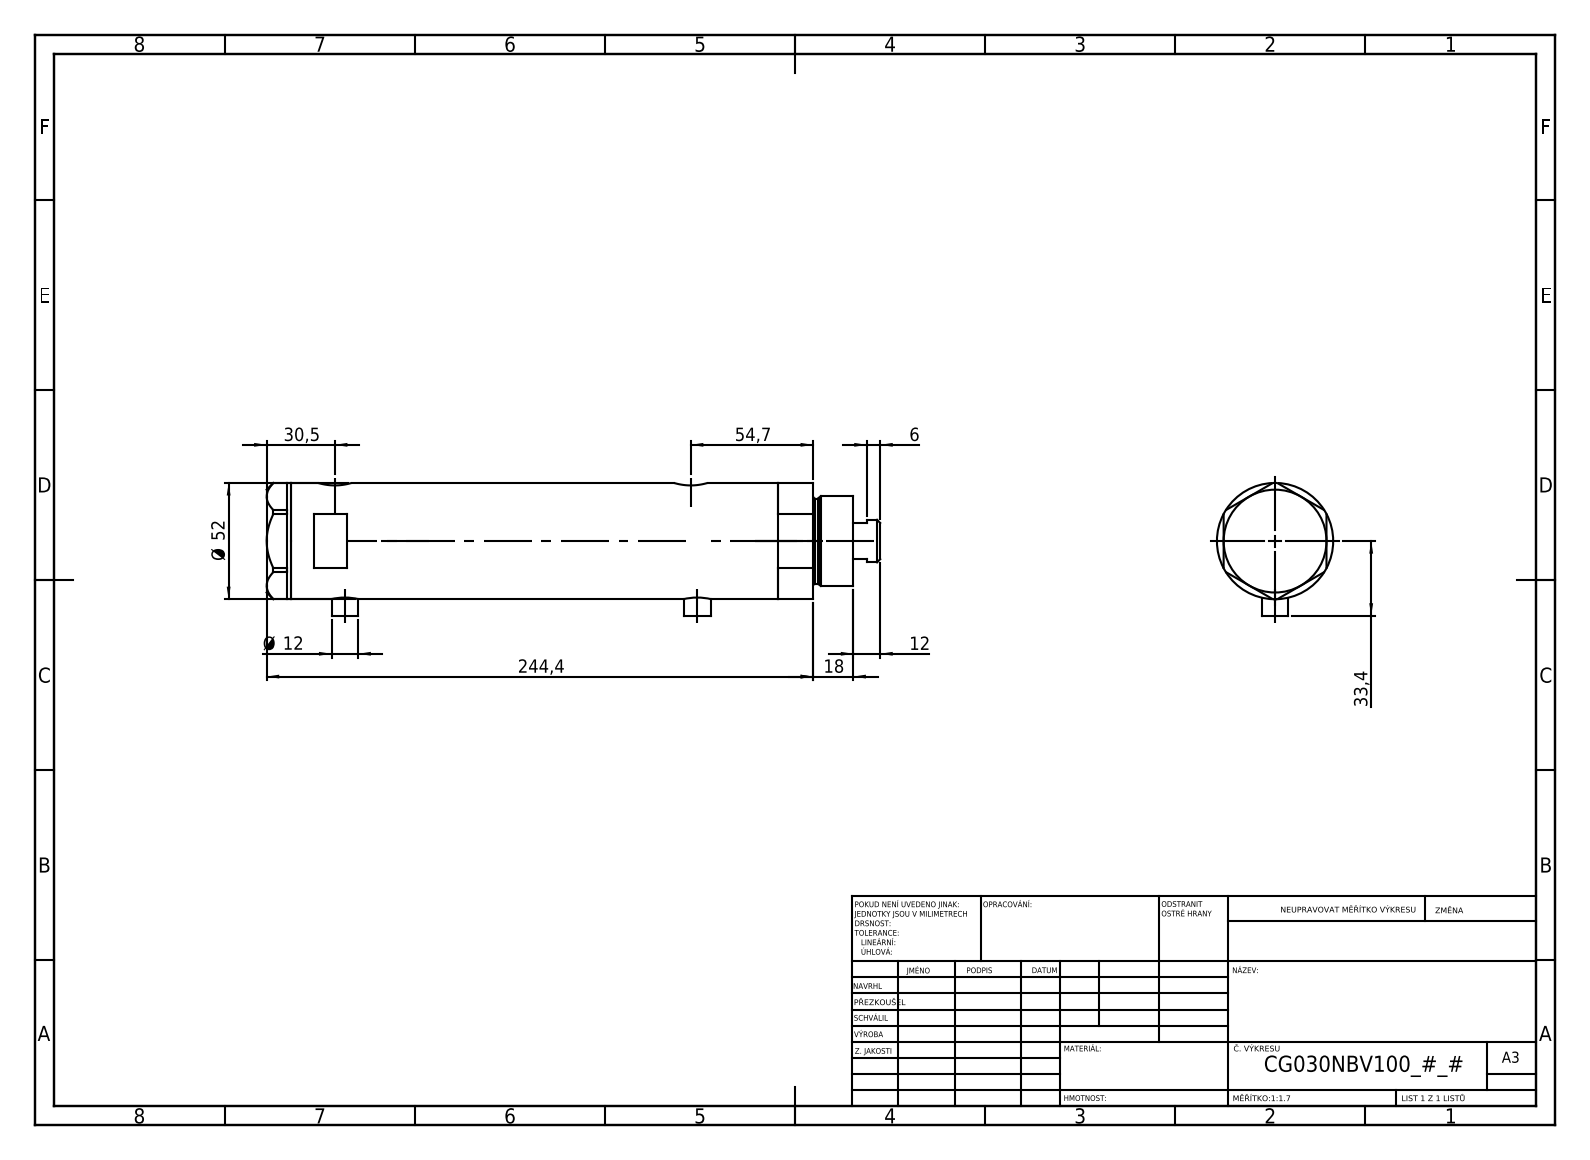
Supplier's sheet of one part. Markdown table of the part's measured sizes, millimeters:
| quantity | value |
| --- | --- |
| part name | V270CG_BACK; V270CG_MIDDLE; V270CG_FRONT; V270CG_VC |
| STEP written by | SolidWorks 2019 (CONFIG_CONTROL_DESIGN) |
| units | millimeters |
| bodies | 4 solids, 134 faces (65 planar, 49 cylindrical, 20 other) |
| overall size | 274.4 × 59.4 × 52 |
| volume | 498 565 mm³ |
| surface area | 106 603 mm² |
| round holes (diameter × count) | 9.73 × 2, 12.5 × 2, 15 × 2, 6.5 × 1, 20 × 1, 21.5 × 1, 30 × 1, 33 × 1, 44 × 1 |
| round bosses / shafts (diameter × count) | 12 × 2, 52 × 1, 40 × 1, 38 × 1, 19 × 1 |
| main face-to-face distances | 181.5, 23.8, 157.7, 11, 34.8, 192.5, 46, 228.9, 217.9, 194.1 |
| hole center spacings | 2.9, 4.5, 154.7, 157.6, 159.2, 162.1 |
